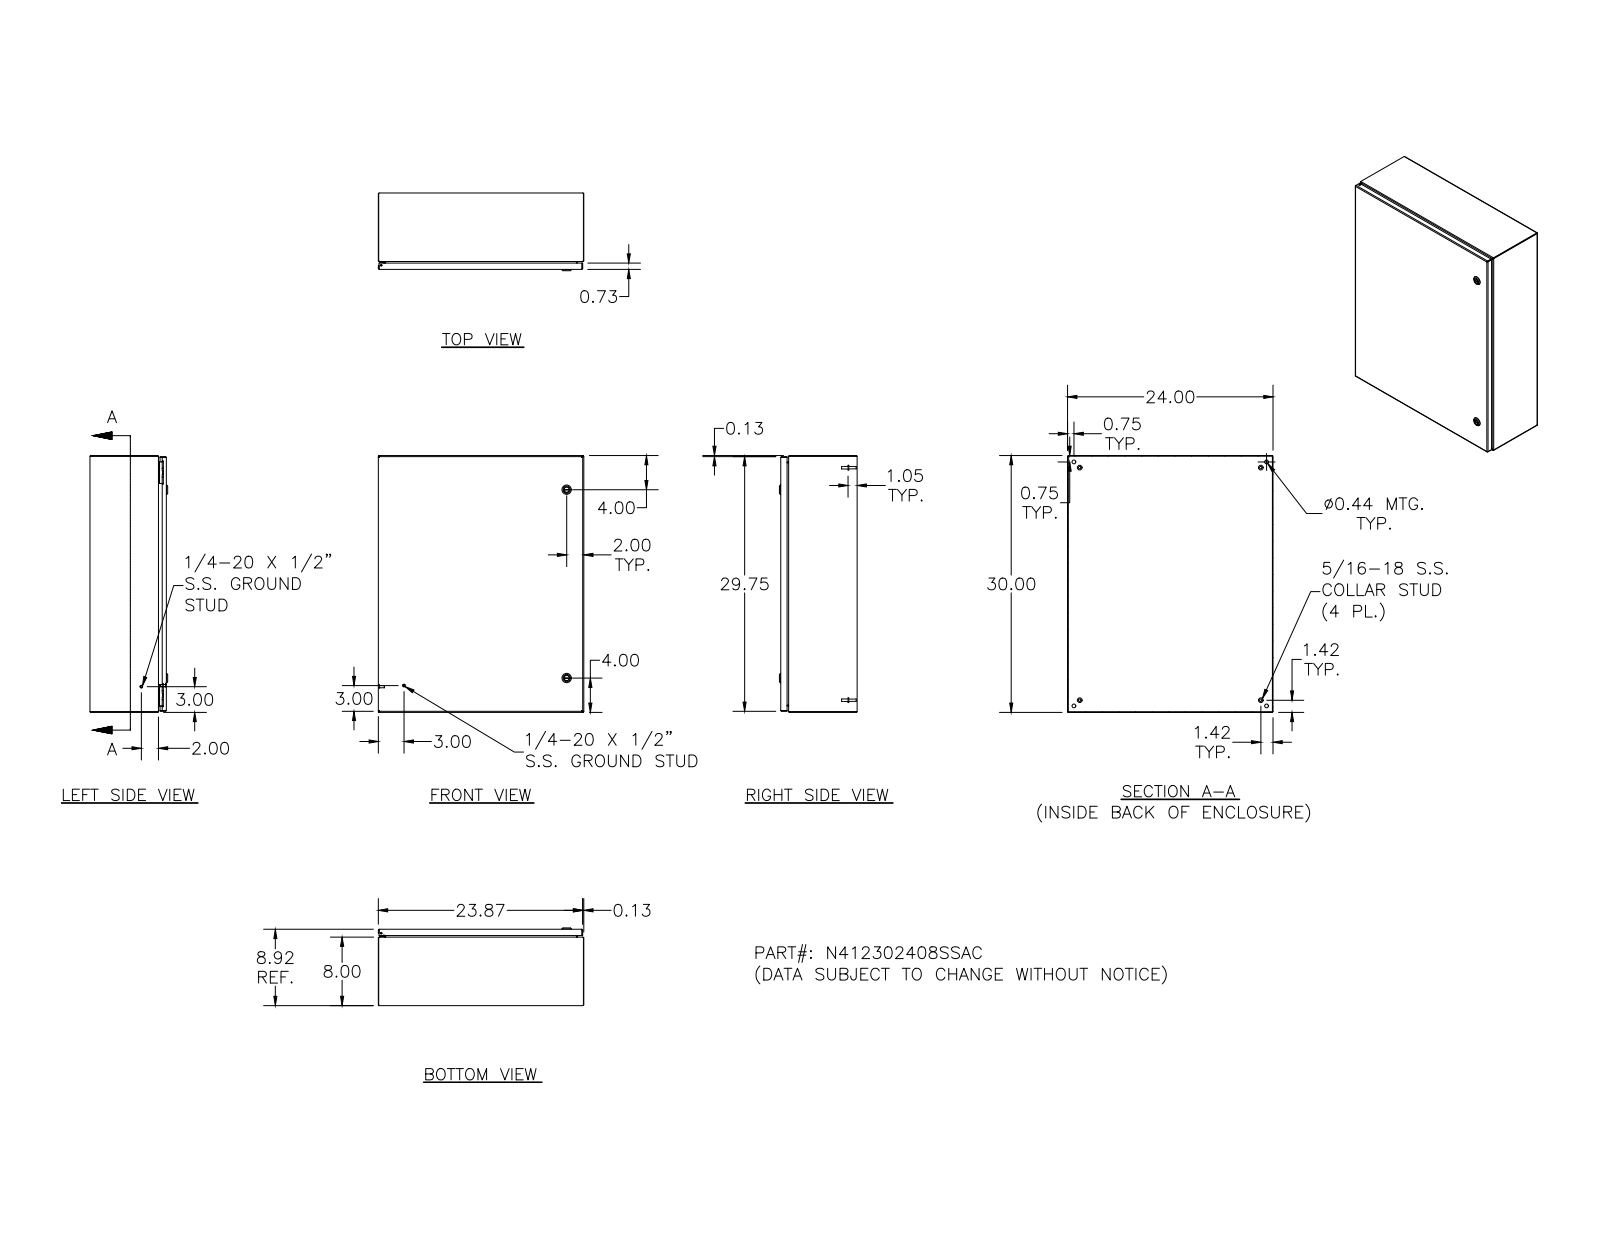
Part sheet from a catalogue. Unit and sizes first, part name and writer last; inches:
Units: inches
Overall size (bounding box): 30 × 24 × 9.075
Round holes (diameter × count): ⌀0.188 ×5, ⌀0.093 ×4, ⌀0.152 ×4, ⌀0.167 ×4, ⌀0.172 ×4, ⌀0.437 ×4, ⌀0.156 ×2, ⌀0.197 ×2, ⌀0.315 ×2, ⌀0.394 ×2, ⌀0.402 ×2, ⌀0.634 ×2
Round bosses / shafts (diameter × count): ⌀0.25 ×10, ⌀0.563 ×4, ⌀0.36 ×4, ⌀0.32 ×4, ⌀0.3 ×4, ⌀0.275 ×4, ⌀0.256 ×4, ⌀0.164 ×4
Partial cylindrical surfaces — rounded edges, fillets, slot ends (radius × count): R0.05 ×26, R0.016 ×18, R0.016 ×16, R0.09 ×16, R0.02 ×15, R0.031 ×14, R0.125 ×14, R0.032 ×8
Main face-to-face distances: 0.074, 8.843, 8.917, 8.769, 23.926, 29.926, 23.852, 24, 30, 29.852
Hole centre spacings: 26, 0.017, 0.66, 22.869, 0.019, 0.5, 0.648, 0.652
Volume: 187.1 in³ · Surface area: 5 074 in²
Bodies: 42 solids, 1662 faces (698 planar, 588 cylindrical, 376 other)
Part name (STEP PRODUCT): N412302408SSAC; N412302408SSACBKP; 388151; N4123024SSACLID (+8 more)
STEP written by: Autodesk Inventor 2011 (AUTOMOTIVE_DESIGN)
